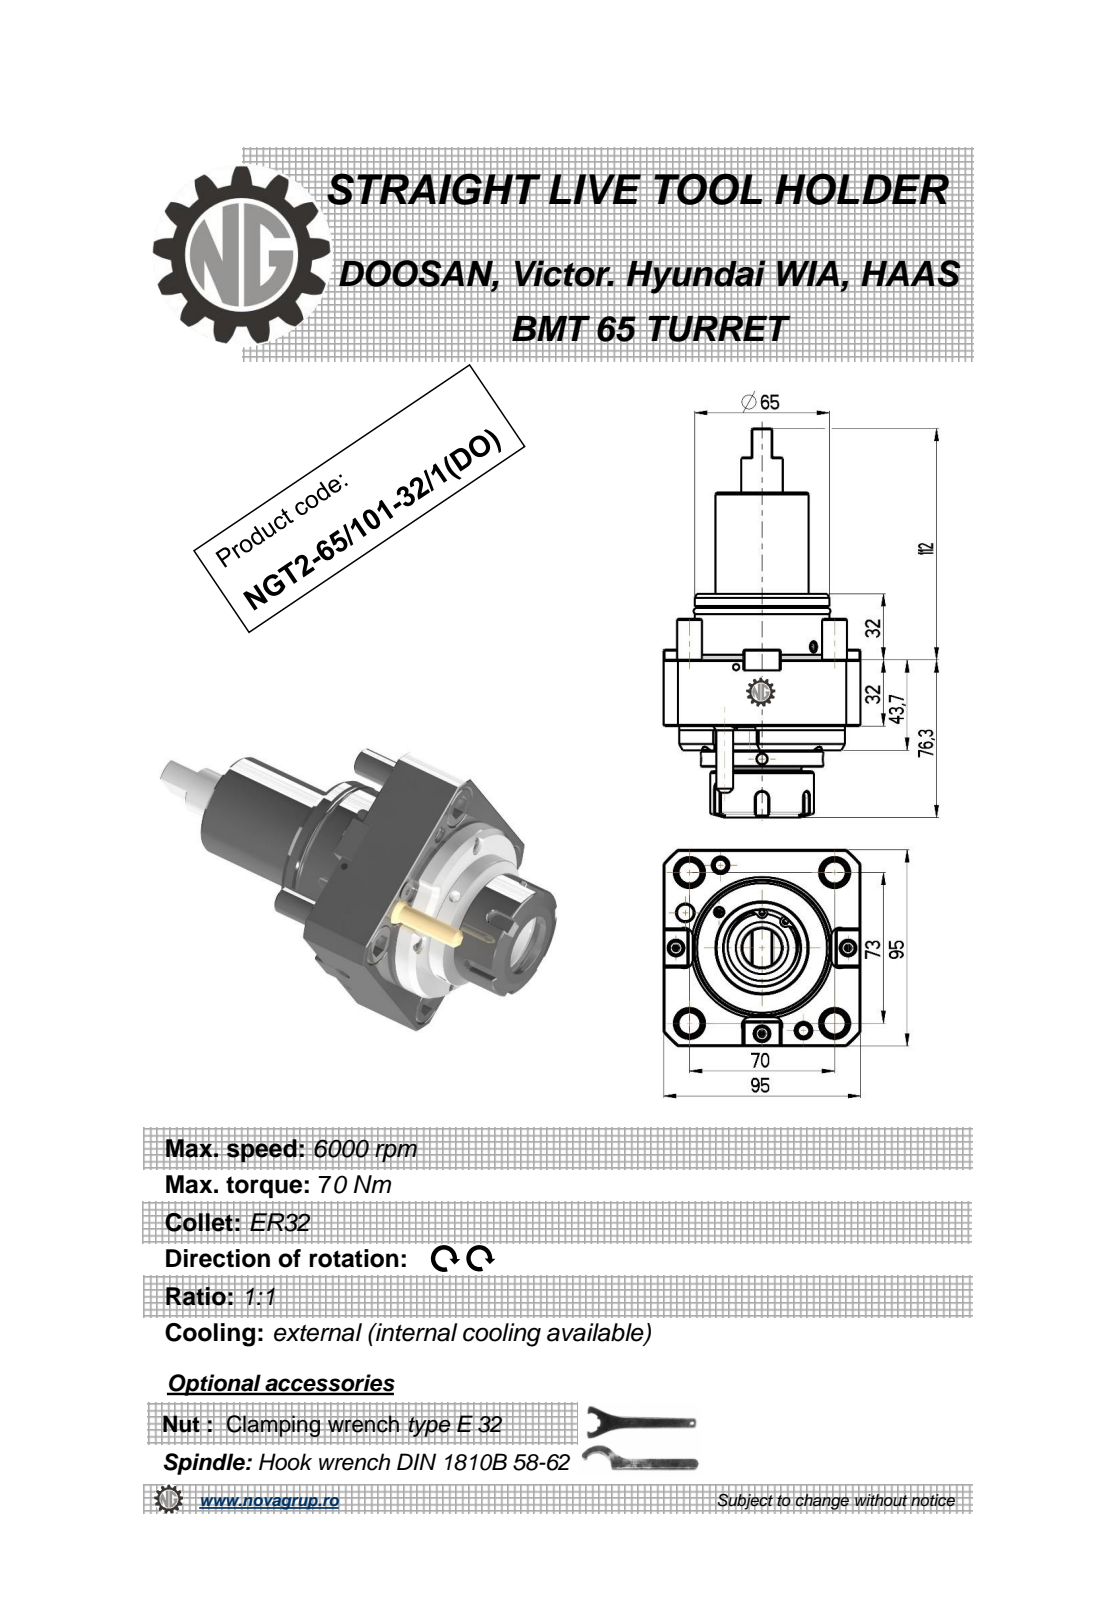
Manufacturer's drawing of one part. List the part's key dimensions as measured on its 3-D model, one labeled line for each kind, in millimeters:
Part name (STEP PRODUCT): NGT2_65_101_32_1_DO
STEP written by: PRO/ENGINEER BY PARAMETRIC TECHNOLOGY CORPORATION, 2010280 (CONFIG_CONTROL_DESIGN)
Units: millimetres
Bodies: 2 solids, 269 faces (115 planar, 66 cylindrical, 88 other)
Overall size (bounding box): 188.3 × 95 × 95
Volume: 609 887 mm³ · Surface area: 64 828 mm²
Round holes (diameter × count): ⌀5 ×3, ⌀3 ×1, ⌀8 ×1, ⌀27 ×1
Round bosses / shafts (diameter × count): ⌀12 ×4, ⌀80 ×1, ⌀65 ×1, ⌀60 ×1, ⌀59 ×1, ⌀50 ×1, ⌀46 ×1, ⌀45 ×1
Partial cylindrical surfaces — rounded edges, fillets, slot ends (radius × count): R0.22 ×6, R3 ×5, R6 ×3, R0.8 ×2, R62.5 ×1
Main face-to-face distances: 32, 95, 43.7, 11.7, 64, 75.7, 8, 83.7, 51.7, 19.7
Hole centre spacings: 40.7, 40.72, 56.77
